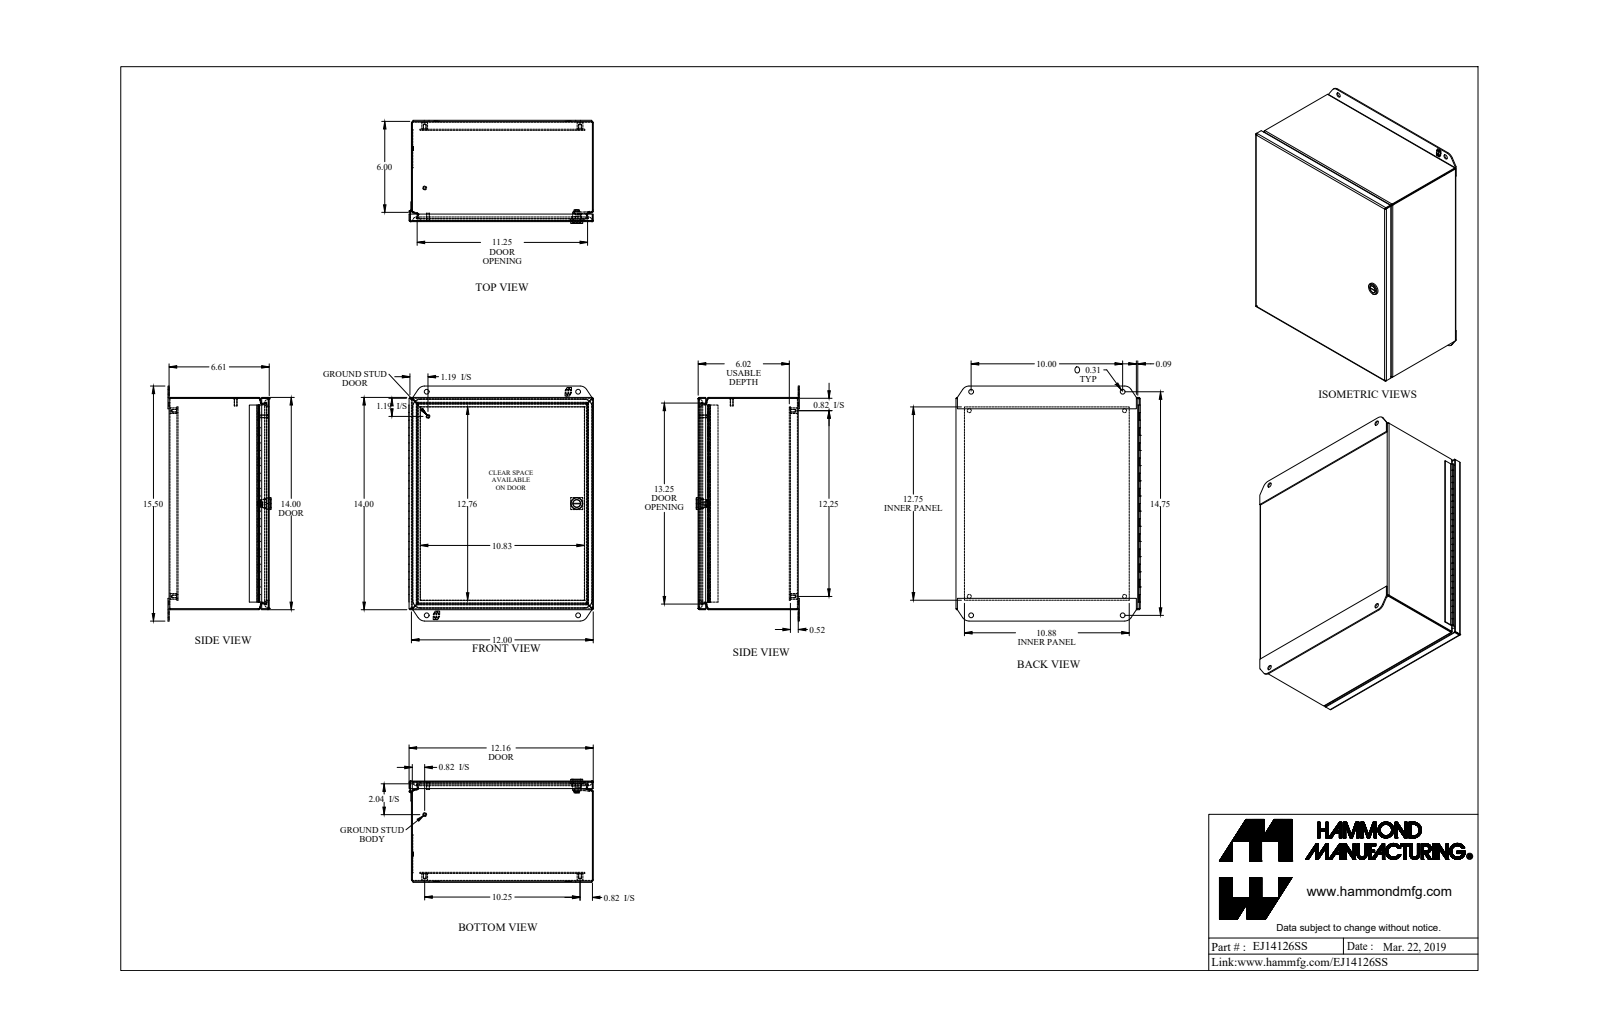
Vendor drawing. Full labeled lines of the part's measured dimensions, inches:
Part name (STEP PRODUCT): EJ14126SS_Default
STEP written by: SolidWorks 2019 (CONFIG_CONTROL_DESIGN)
Units: inches
Bodies: 16 solids, 752 faces (418 planar, 238 cylindrical, 96 other)
Overall size (bounding box): 15.5 × 12.165 × 6.805
Volume: 58.2 in³ · Surface area: 1 922 in²
Round holes (diameter × count): ⌀0.156 ×4, ⌀0.265 ×4, ⌀0.313 ×4, ⌀0.05 ×1, ⌀0.516 ×1
Round bosses / shafts (diameter × count): ⌀0.375 ×4, ⌀0.25 ×2, ⌀0.19 ×2, ⌀0.788 ×1, ⌀0.535 ×1, ⌀0.496 ×1, ⌀0.435 ×1, ⌀0.1 ×1
Partial cylindrical surfaces — rounded edges, fillets, slot ends (radius × count): R0.029 ×16, R0.086 ×16, R0.281 ×12, R0.25 ×4, R0.499 ×4, R0.5 ×4, R0.06 ×2, R0.03 ×1
Main face-to-face distances: 0.057, 6.554, 0.072, 0.589, 6.611, 6.497, 11.943, 13.943, 6.094, 6.037
Hole centre spacings: 1.257, 10.202, 13.5, 16.875, 6.129, 7.376, 10, 10.25
